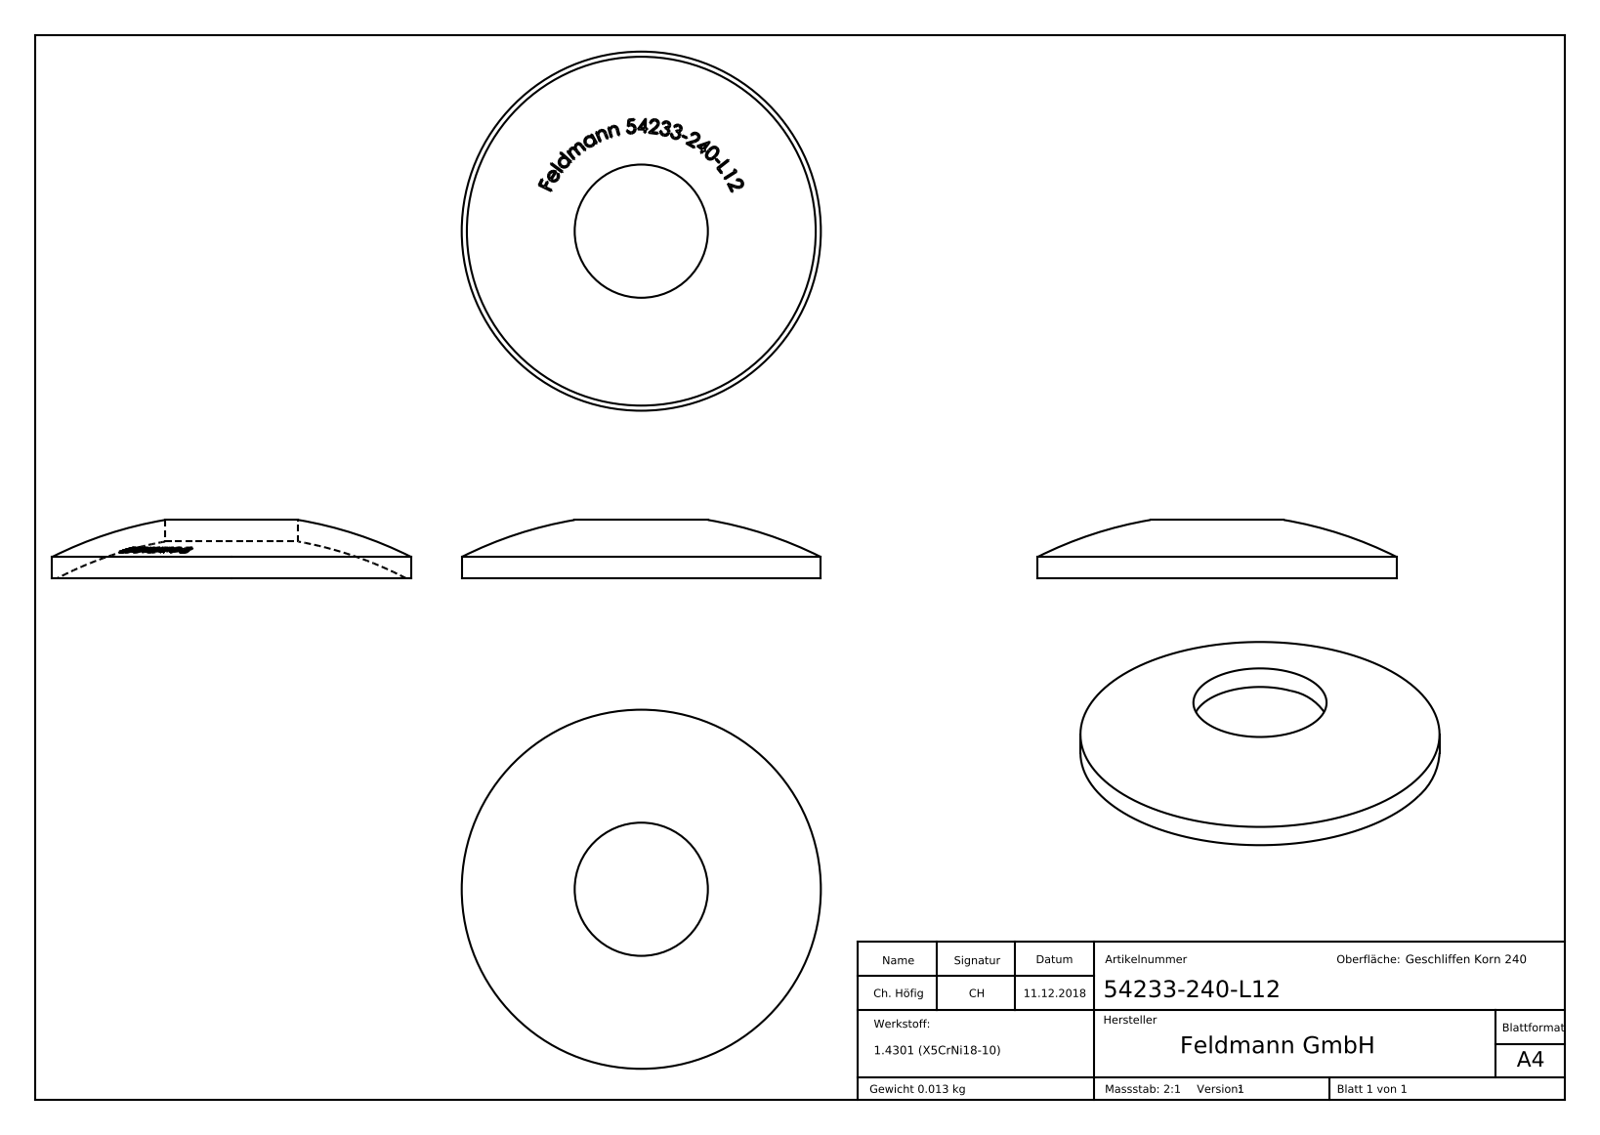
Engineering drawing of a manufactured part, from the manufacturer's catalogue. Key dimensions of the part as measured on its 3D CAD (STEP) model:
Part name (STEP PRODUCT): 54233-240-L12
STEP written by: SolidWorks 2015 (CONFIG_CONTROL_DESIGN)
Units: millimetres
Bodies: 1 solid, 269 faces (144 planar, 4 cylindrical, 121 other)
Overall size (bounding box): 33.7 × 33.7 × 5.47
Volume: 1 636 mm³ · Surface area: 1 940 mm²
Round holes (diameter × count): ⌀12.5 ×1
Round bosses / shafts (diameter × count): ⌀33.7 ×1
Main face-to-face distances: 0.54, 0.72, 0.66, 0.84, 0.67, 0.78, 1.45, 1.33, 1.32, 1.2
